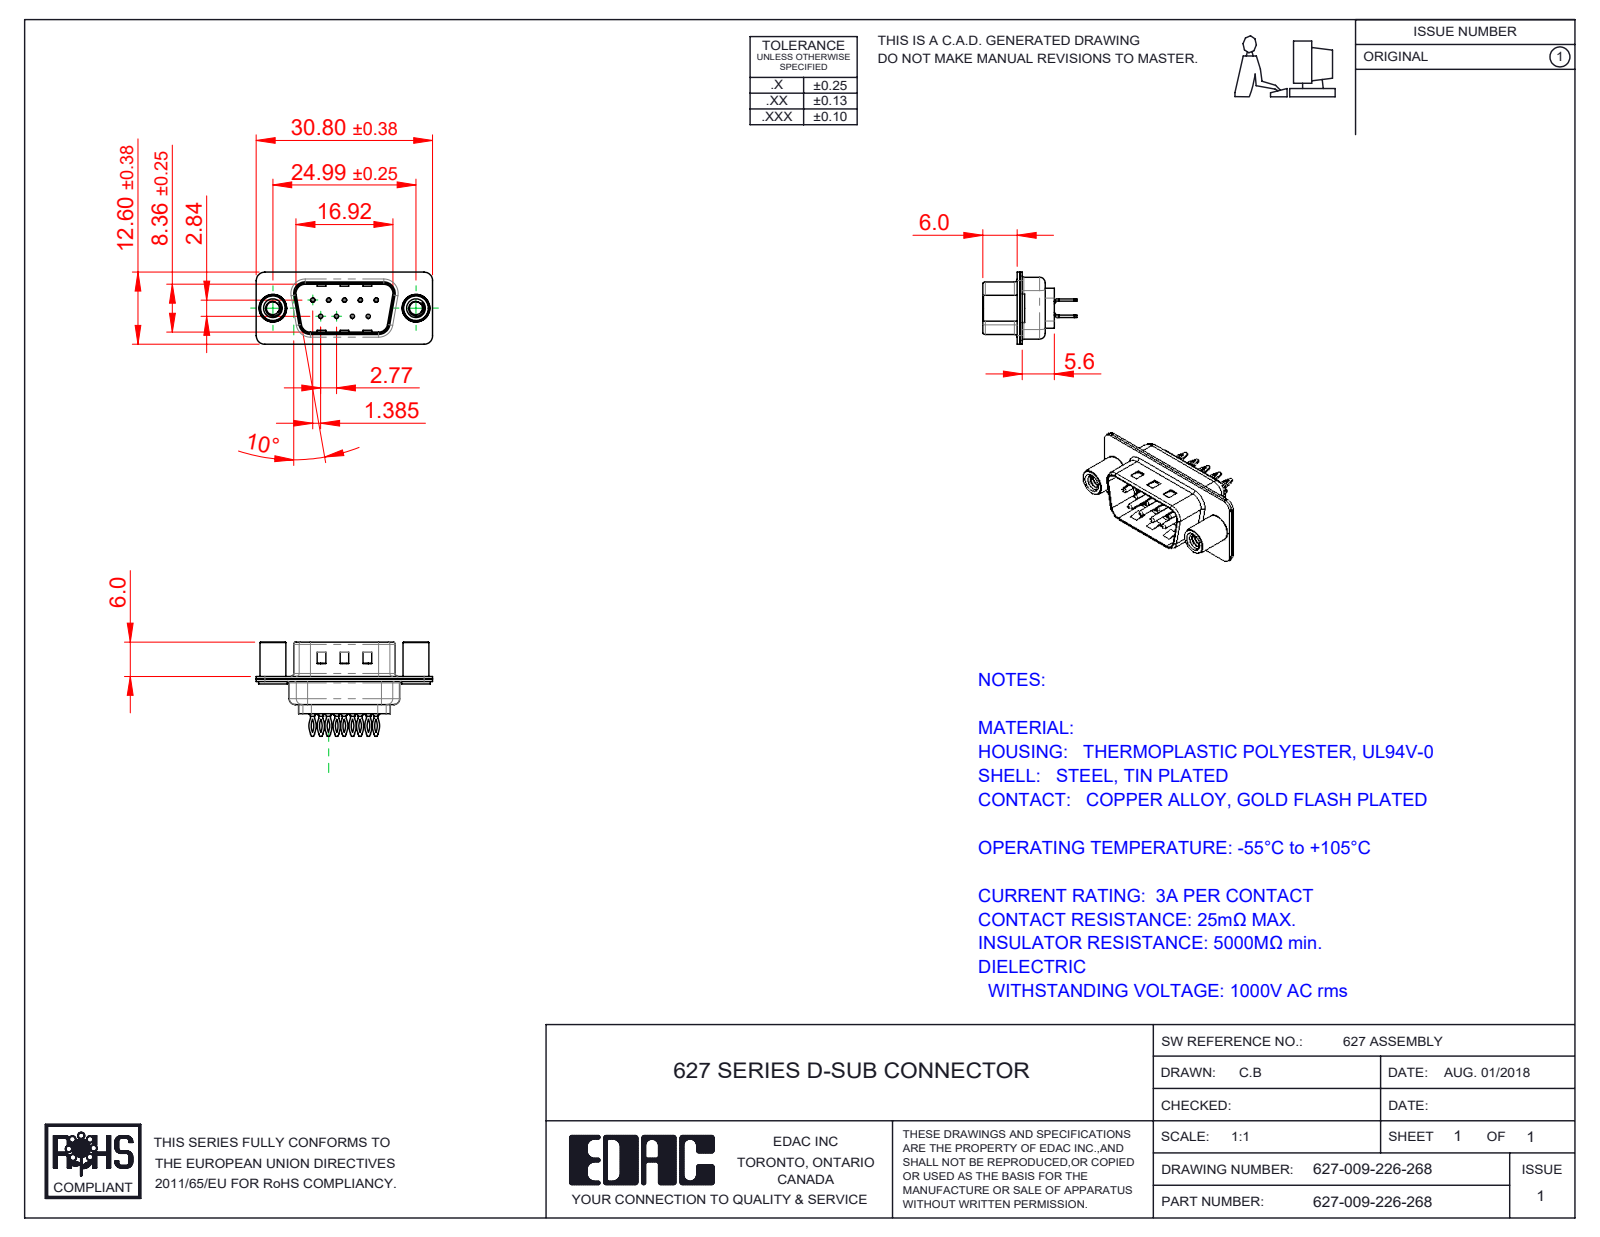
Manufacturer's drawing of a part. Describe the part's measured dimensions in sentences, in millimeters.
The part is named "627 4-40 Threaded Standoff; 627 Contact Row 2_26L; 627-009-226-268; 627 Housing_09 LP (+3 more)". Its 3-D file was written by "SolidWorks 2020 (CONFIG_CONTROL_DESIGN)". It is 14 solids with 1022 faces: 289 planar, 436 cylindrical and 297 other. Overall it measures 30.8 by 16.45 by 12.6 millimeters. Its volume is 1 375 cubic millimeters and its surface area 4 100 square millimeters. Round holes: 9 of diameter 0.35, 9 of diameter 1.1, 9 of diameter 1.6, 2 of diameter 2.26, 2 of diameter 4, 2 of diameter 4.8. Round bosses or shafts: 9 of diameter 2, 9 of diameter 1.5, 9 of diameter 0.75, 2 of diameter 5, 2 of diameter 4.9, 2 of diameter 4.5. Partial cylindrical surfaces (rounded edges, fillets, slot ends): 18 of radius 1.5, 18 of radius 2.92, 18 of radius 3.33, 12 of radius 2, 8 of radius 0.5, 8 of radius 1.6, 4 of radius 0.25, 4 of radius 0.6. The main face-to-face distances are 0.4, 0.45, 0.9, 0.82, 9.58, 1.4, 8.76, 0.5, 1.5, 6.05. The hole center spacings are 3.16, 2.77, 5.54, 5.03, 5.04, 8.31, 7.48, 7.49.
